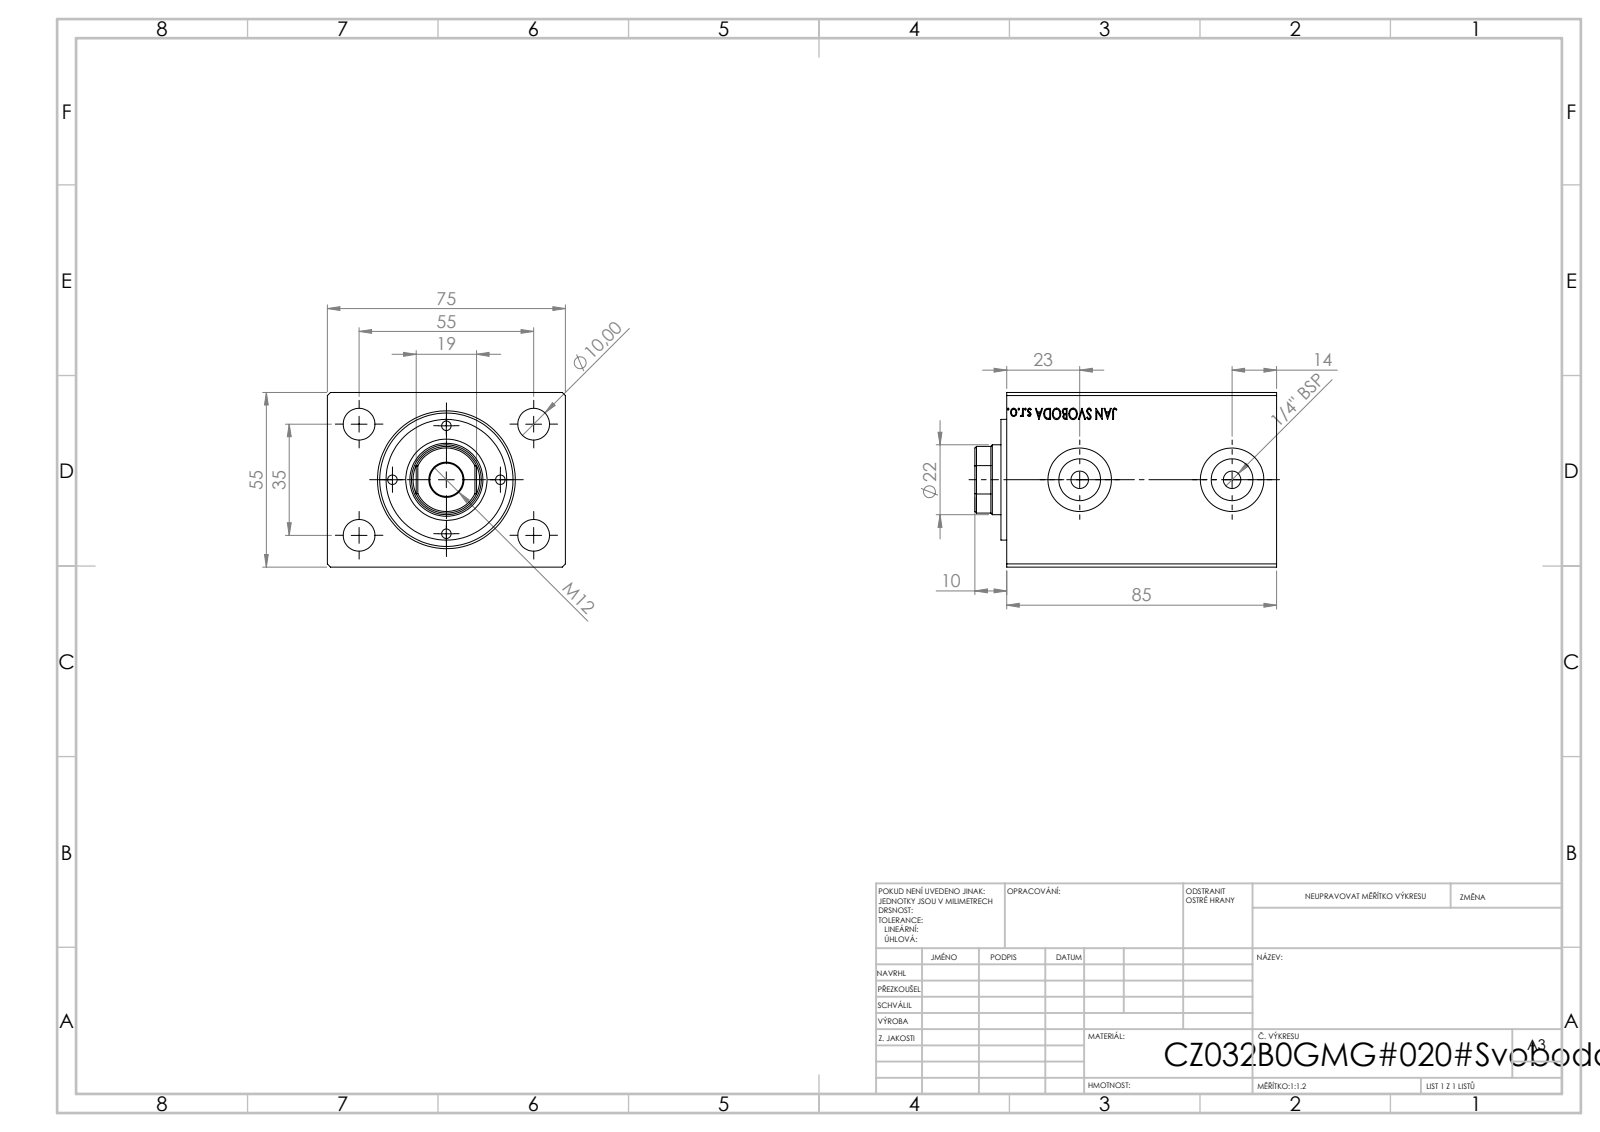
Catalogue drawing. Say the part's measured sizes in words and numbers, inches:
The part is named "V500CZ; V500CZ_B_VC". Its 3-D file was written by "SolidWorks 2019 (CONFIG_CONTROL_DESIGN)". It is 3 solids with 874 faces: 400 planar, 58 cylindrical and 416 other. Overall it measures 3.74 by 2.953 by 2.165 inches. Its volume is 19.72 cubic inches and its surface area 90.5 square inches. Round holes: 4 of diameter 0.118, 4 of diameter 0.394, 2 of diameter 0.217, 2 of diameter 0.518, 2 of diameter 0.787, 1 of diameter 0.413, 1 of diameter 0.866, 1 of diameter 0.906, 1 of diameter 1.26, 1 of diameter 1.417, 1 of diameter 1.654. Round bosses or shafts: 1 of diameter 1.496. Partial cylindrical surfaces (rounded edges, fillets, slot ends): 1 of radius 0.413. The main face-to-face distances are 2.165, 2.953, 3.346, 2.803, 0.543, 0.394, 0.323, 0.071, 3.339, 0.535. The hole center spacings are 0.669, 0.804, 0.946, 1.083, 1.283, 1.737, 1.883, 1.339.
